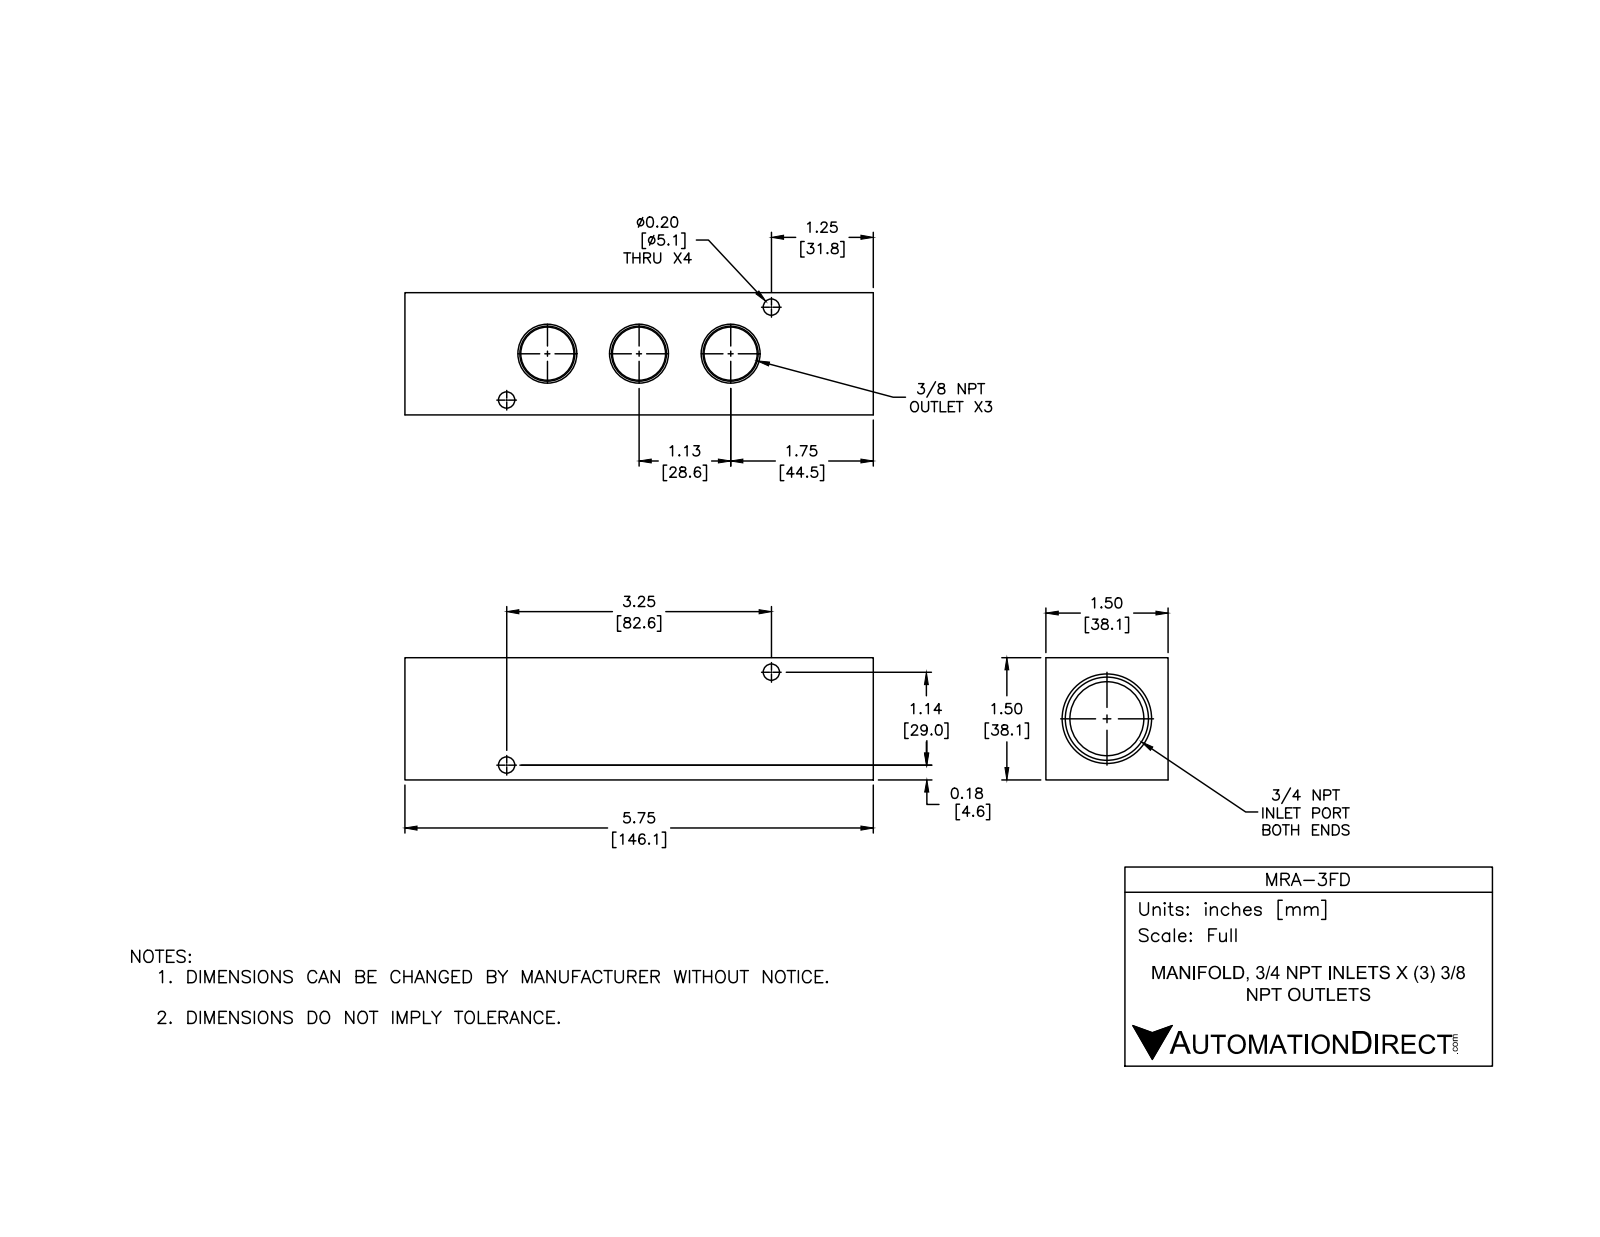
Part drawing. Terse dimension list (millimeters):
name: MRA-3FD
written by: SolidWorks 2015 (CONFIG_CONTROL_DESIGN)
unit: mm
bodies: 1 solid, 52 faces (14 planar, 18 cylindrical, 20 other)
size: 146.1 × 38.1 × 38.1
volume: 139 100 mm³; area: 37 150 mm²
holes: 4× ⌀5.1, 1× ⌀23
face distances: 38.1, 146.1, 14, 132.1, 118.1, 27.7, 10.4
hole spacings: 87.5
